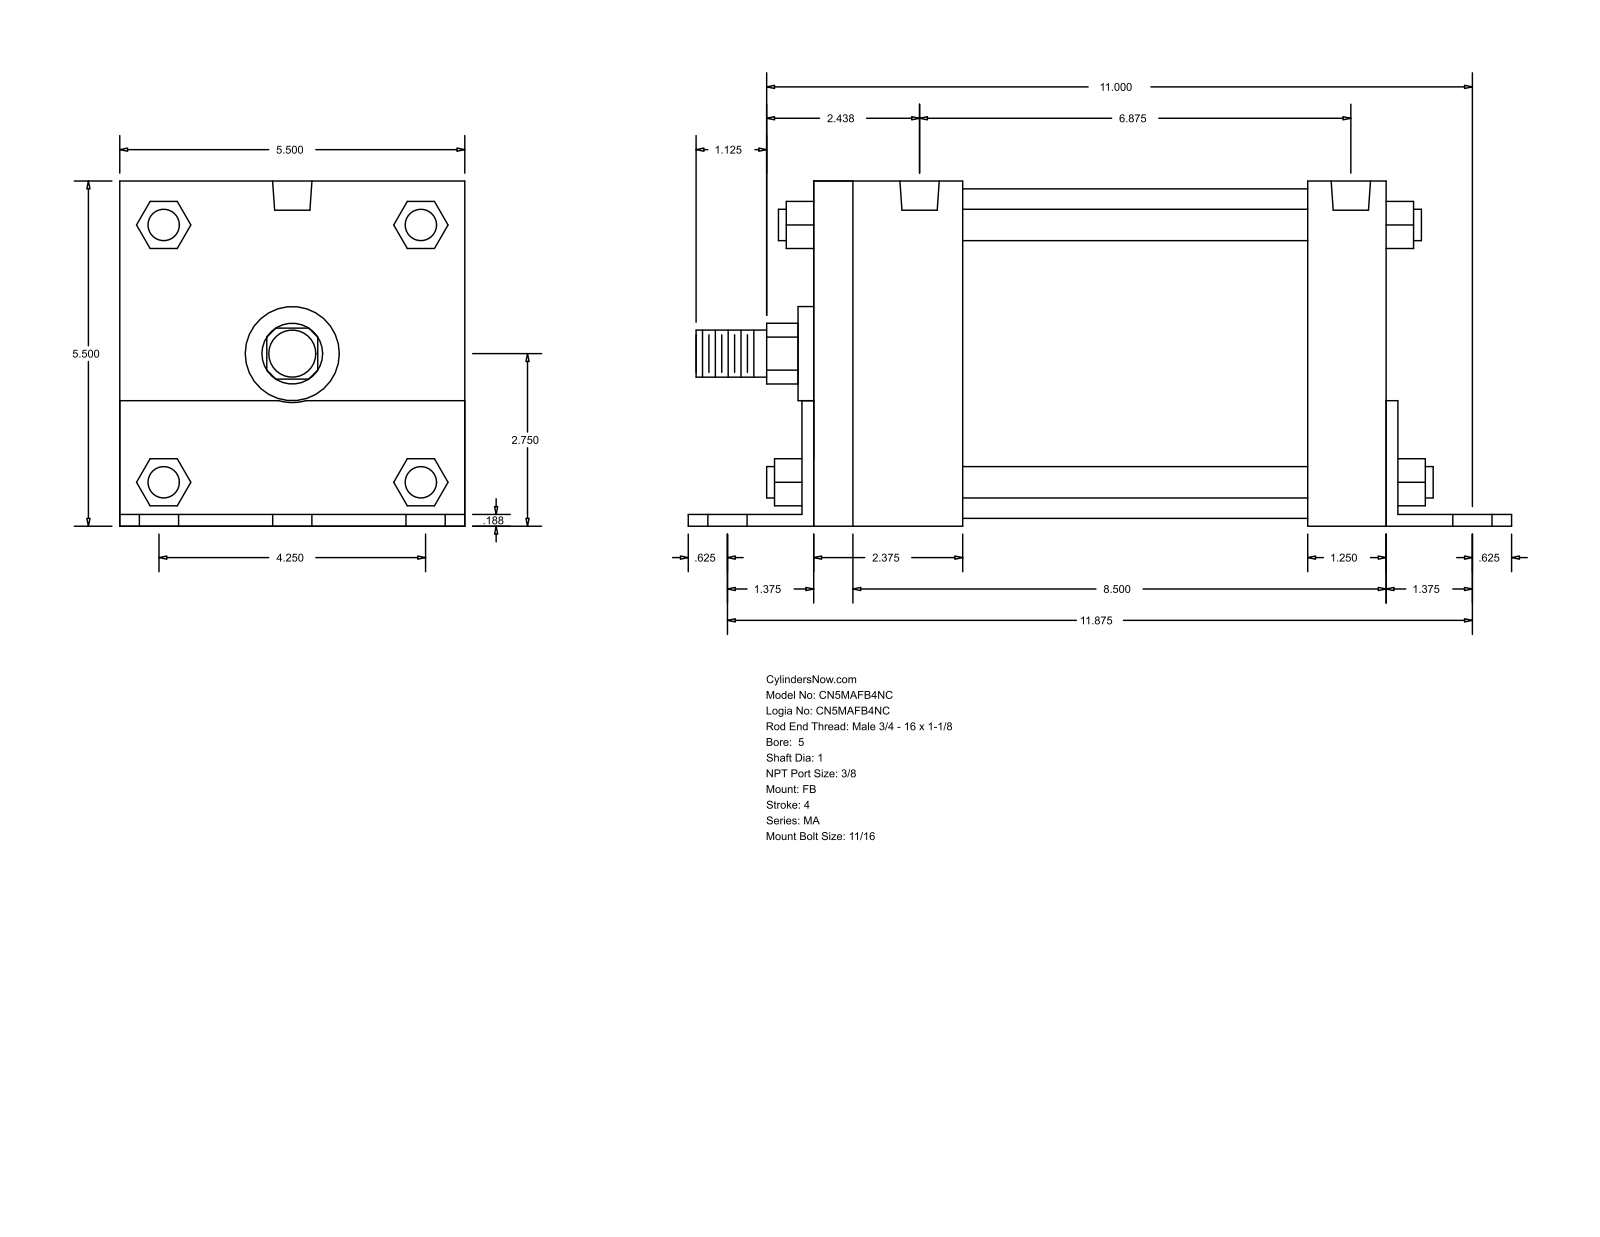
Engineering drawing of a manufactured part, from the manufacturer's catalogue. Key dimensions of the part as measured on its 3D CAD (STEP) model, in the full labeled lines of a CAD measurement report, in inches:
Part name (STEP PRODUCT): MA_FB__0500_1
STEP written by: GSSL Pune (CONFIG_CONTROL_DESIGN)
Units: inches
Bodies: 0 solids, 140 faces (105 planar, 35 cylindrical, 0 other)
Overall size (bounding box): 13.125 × 5.502 × 5.5
Round holes (diameter × count): ⌀0.687 ×6, ⌀0.437 ×4, ⌀0.627 ×2
Round bosses / shafts (diameter × count): ⌀0.5 ×4, ⌀5.25 ×1, ⌀1.5 ×1, ⌀1 ×1, ⌀0.75 ×1
Partial cylindrical surfaces — rounded edges, fillets, slot ends (radius × count): R0.484 ×1, R0.78 ×1
Main face-to-face distances: 5.5, 0.187, 5.502, 0.185, 5.315, 9.125, 0.188, 9.313, 9.312, 9.5
Hole centre spacings: 2.125, 12.064, 11.875, 0.187, 2.876, 3.005, 3.728, 3.883
